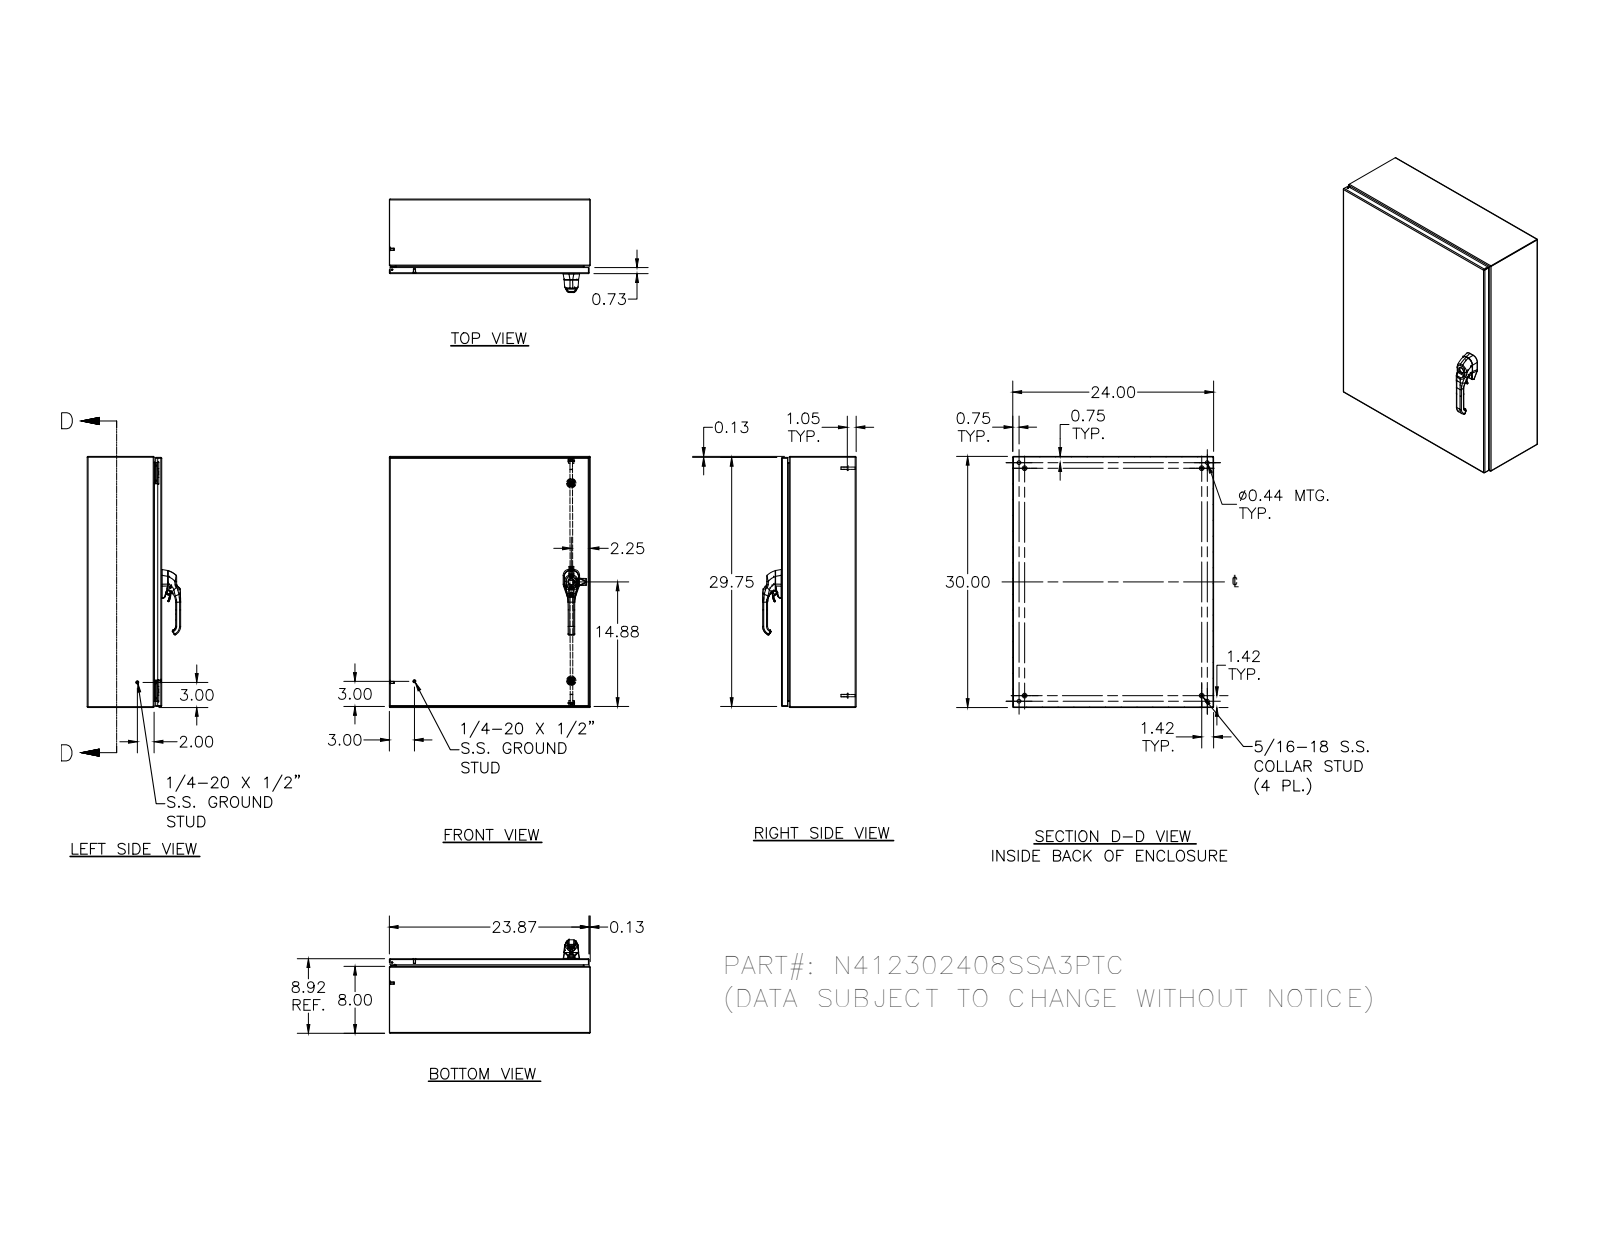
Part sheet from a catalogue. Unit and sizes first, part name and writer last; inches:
Units: inches
Overall size (bounding box): 30 × 24 × 11.166
Round holes (diameter × count): ⌀0.165 ×5, ⌀0.188 ×5, ⌀0.093 ×4, ⌀0.152 ×4, ⌀0.167 ×4, ⌀0.172 ×4, ⌀0.197 ×4, ⌀0.437 ×4, ⌀0.213 ×3, ⌀0.106 ×2, ⌀0.156 ×2, ⌀0.16 ×2
Round bosses / shafts (diameter × count): ⌀0.25 ×10, ⌀0.236 ×6, ⌀0.591 ×4, ⌀0.563 ×4, ⌀0.36 ×4, ⌀0.32 ×4, ⌀0.31 ×4, ⌀0.3 ×4
Partial cylindrical surfaces — rounded edges, fillets, slot ends (radius × count): R0.02 ×180, R0.012 ×101, R0.031 ×30, R0.05 ×26, R0.118 ×23, R0.019 ×21, R0.105 ×20, R0.016 ×18
Main face-to-face distances: 0.074, 8.843, 8.917, 8.769, 23.926, 29.926, 23.852, 24, 30, 29.852
Hole centre spacings: 25.996, 22.869, 0.017, 0.66, 1.618, 26.656, 0.019, 0.5
Volume: 197.3 in³ · Surface area: 5 205 in²
Bodies: 63 solids, 3088 faces (1046 planar, 1119 cylindrical, 923 other)
Part name (STEP PRODUCT): N412302408SSA3PTC; N412302408SSA3PTCBKP; N4123024SSA3PTCLID; HFW328176 (+8 more)
STEP written by: Autodesk Inventor 2011 (AUTOMOTIVE_DESIGN)
